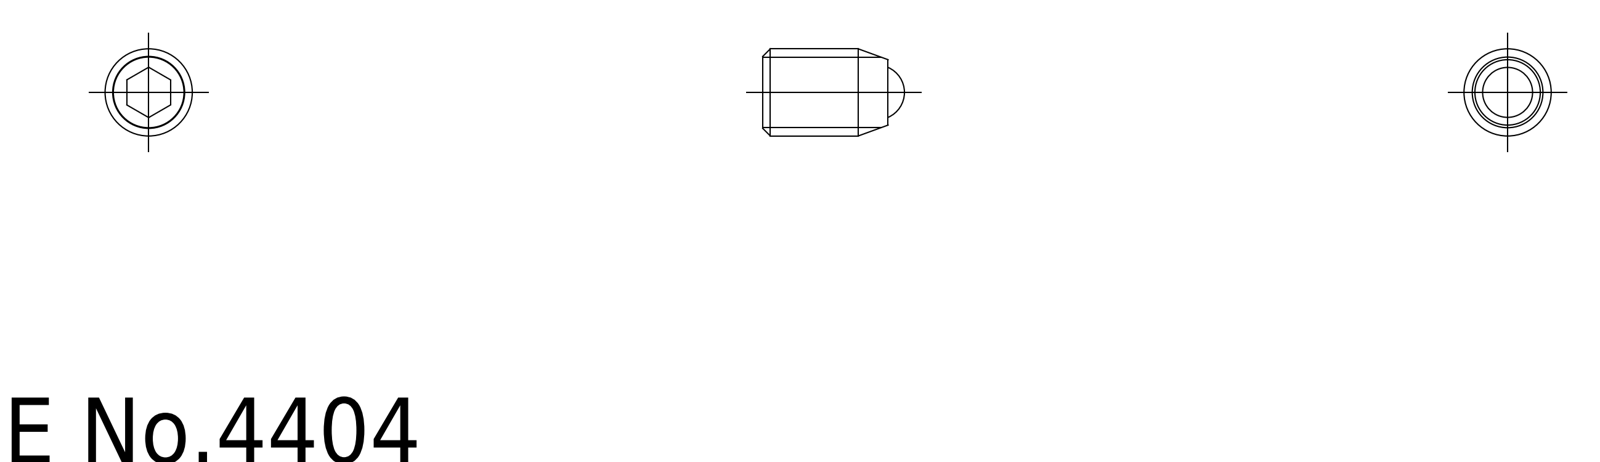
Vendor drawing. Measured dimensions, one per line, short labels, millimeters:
name: ball; SCSS_M4_6_R_18792_36
written by: CADfix (AUTOMOTIVE_DESIGN)
unit: mm
bodies: 2 solids, 20 faces (0 planar, 0 cylindrical, 20 other)
size: 6.5 × 4 × 4
volume: 56 mm³; area: 144 mm²
